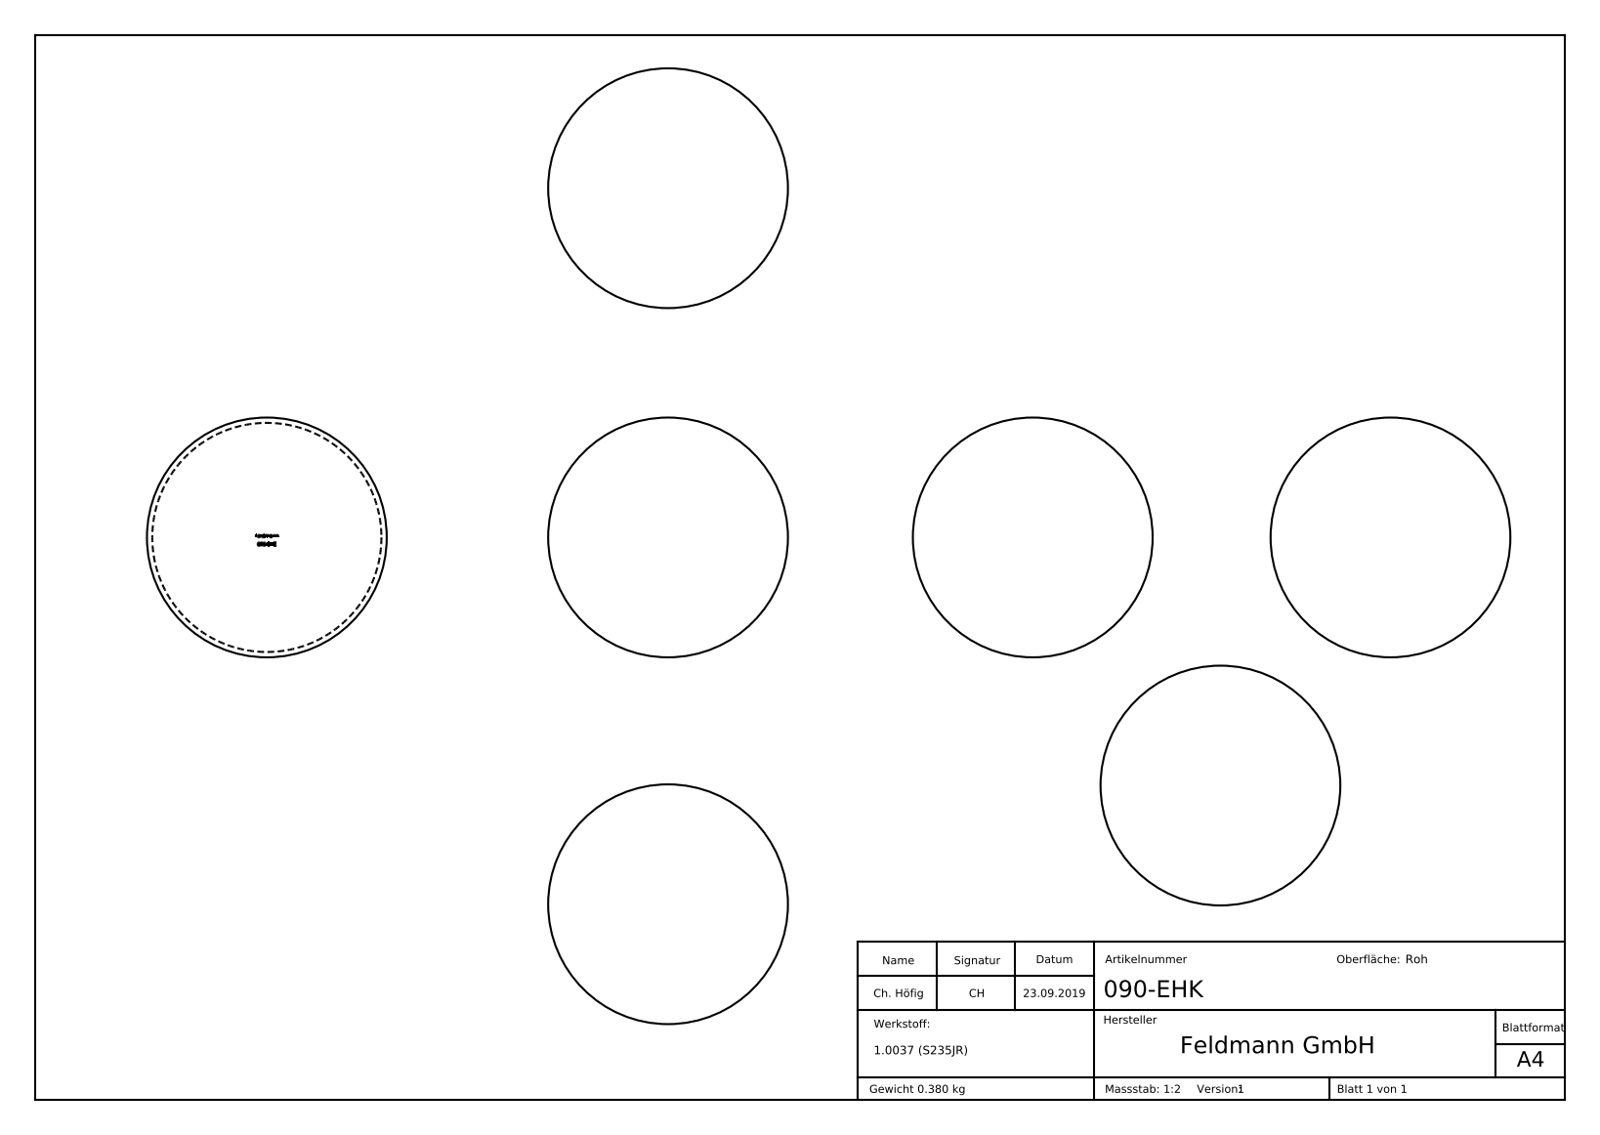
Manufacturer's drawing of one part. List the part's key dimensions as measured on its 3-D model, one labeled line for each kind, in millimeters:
Part name (STEP PRODUCT): 090-EHK
STEP written by: SolidWorks 2015 (CONFIG_CONTROL_DESIGN)
Units: millimetres
Bodies: 1 solid, 198 faces (96 planar, 0 cylindrical, 102 other)
Overall size (bounding box): 90 × 90 × 90
Volume: 48 665 mm³ · Surface area: 48 691 mm²
Main face-to-face distances: 3.2, 1.26, 3.13, 4.5, 0.46, 1.35, 3.59, 0.68, 0.64, 3.47
